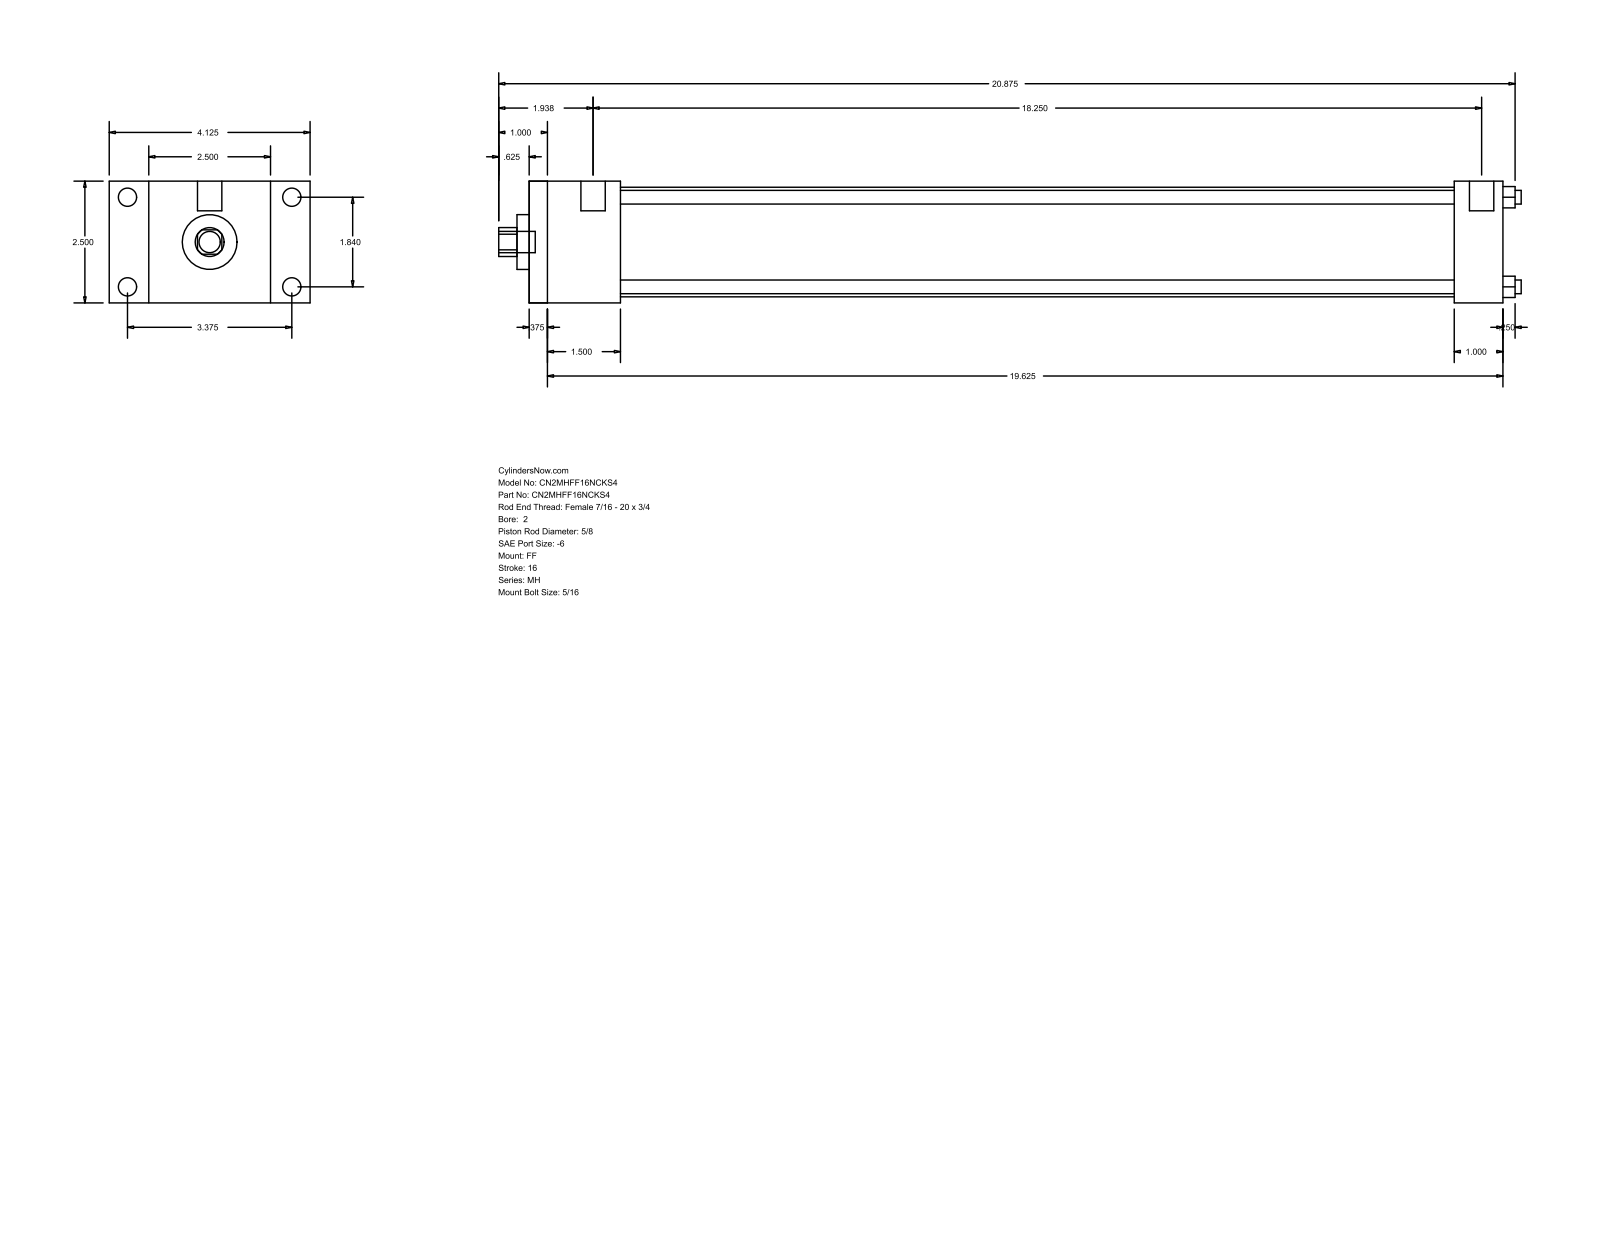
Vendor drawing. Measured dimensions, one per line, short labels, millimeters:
name: MH_FF__0200_0.625
written by: GSSL Pune (CONFIG_CONTROL_DESIGN)
unit: mm
bodies: 0 solids, 92 faces (64 planar, 28 cylindrical, 0 other)
size: 533.4 × 104.78 × 63.5
holes: 4× ⌀7.14, 1× ⌀15.88, 1× ⌀28.57, 1× ⌀57.15
bosses: 4× ⌀9.53, 4× ⌀5.56, 2× ⌀12.7, 1× ⌀11.11
rounds: 1× R7.54
face distances: 63.5, 508, 9.52, 498.48, 25.4, 38.1, 47.62, 482.6, 473.08, 434.98
hole spacings: 33.05, 46.74, 66.1
